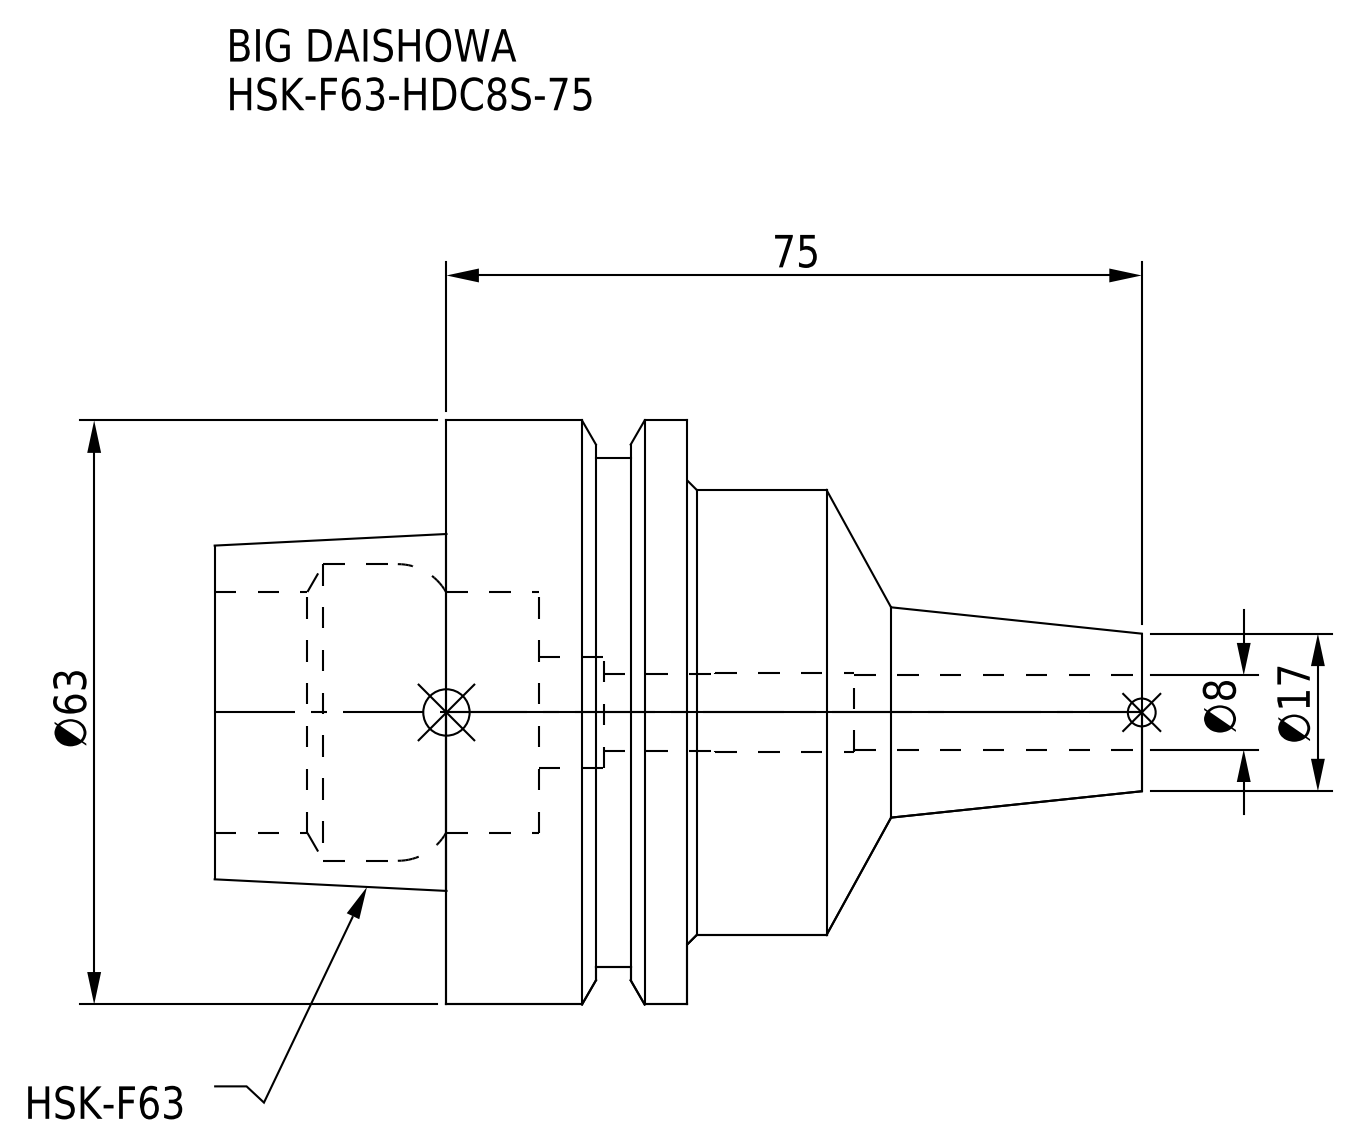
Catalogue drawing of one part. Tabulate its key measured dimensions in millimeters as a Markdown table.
| quantity | value |
| --- | --- |
| part name | HSK-F63-HDC8S-75 |
| STEP written by | CREO PARAMETRIC BY PTC INC, 2016380 (AUTOMOTIVE_DESIGN) |
| units | millimeters |
| bodies | 1 solid, 50 faces (10 planar, 24 cylindrical, 16 other) |
| overall size | 100 × 63 × 63 |
| volume | 121 718 mm³ |
| surface area | 24 009 mm² |
| round holes (diameter × count) | 8 × 1, 8.25 × 1, 8.5 × 1, 12 × 1, 26 × 1, 32 × 1 |
| round bosses / shafts (diameter × count) | 63 × 1, 55 × 1, 48 × 1 |
| main face-to-face distances | 26, 51, 25, 16.05, 9.95, 34.95, 6.12, 9.93, 19.88, 44.88 |
